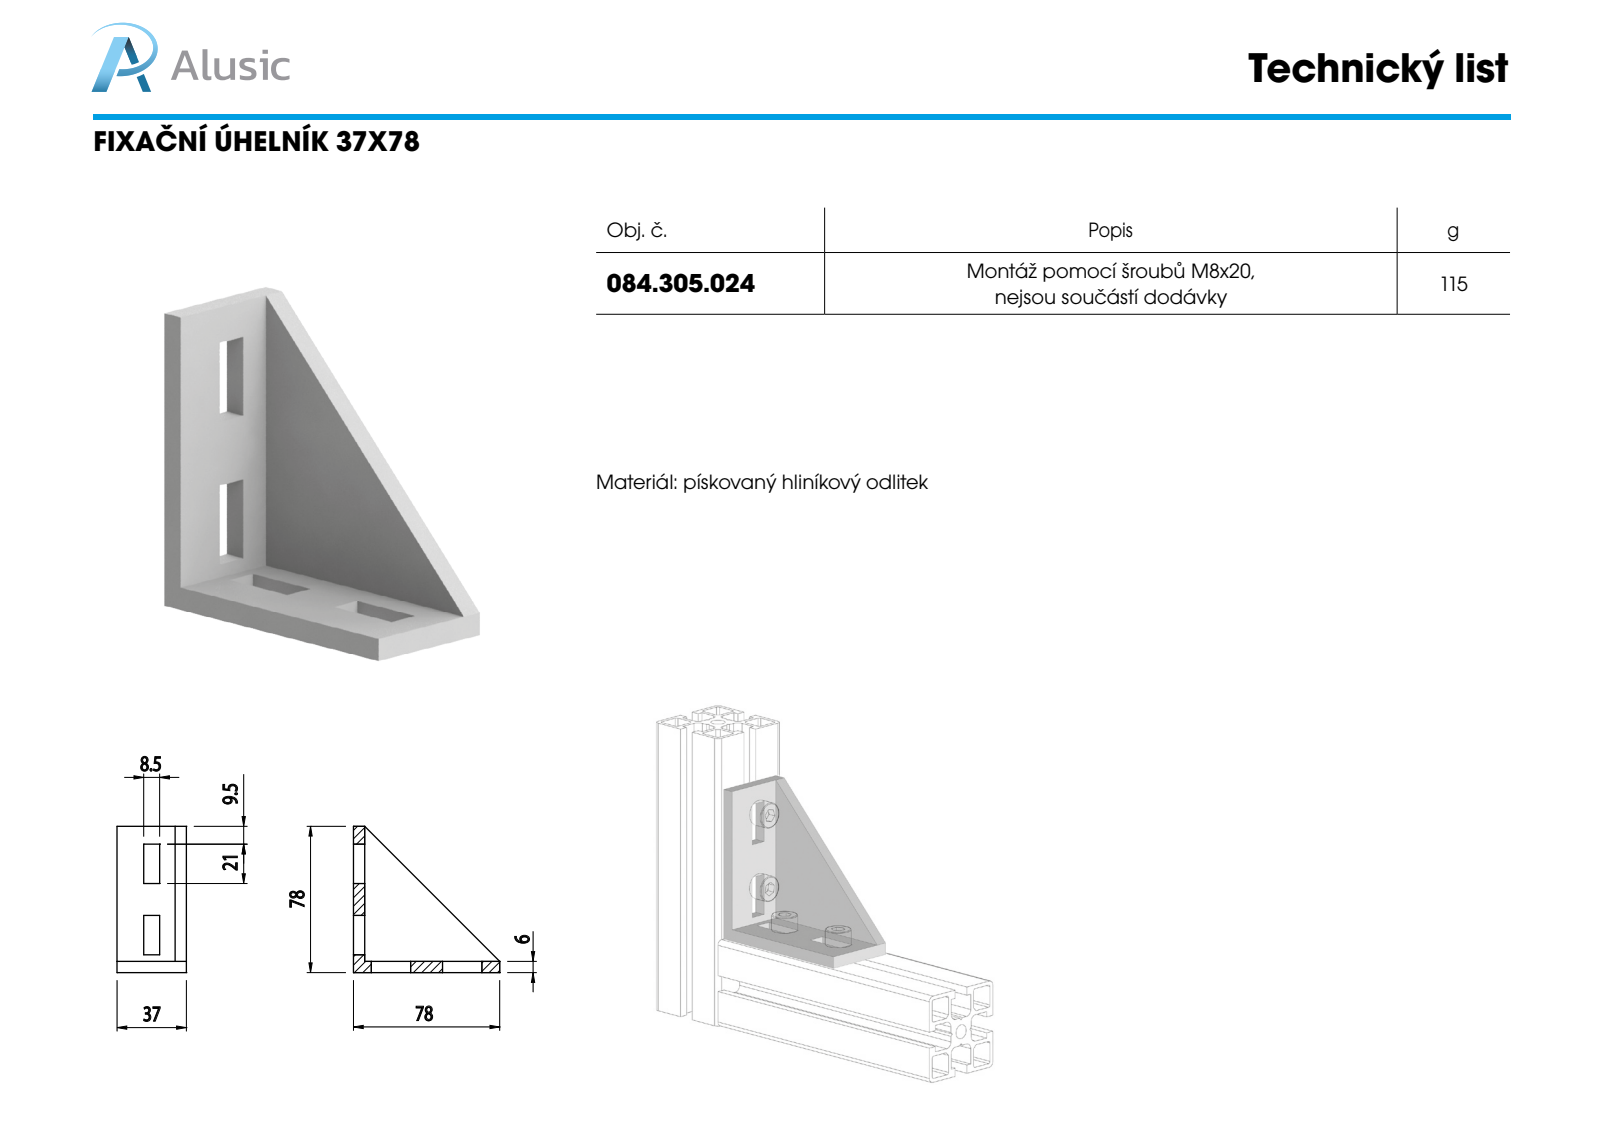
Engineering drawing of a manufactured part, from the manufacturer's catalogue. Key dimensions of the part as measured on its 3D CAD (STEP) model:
Part name (STEP PRODUCT): 084.305.024
STEP written by: SolidWorks 2011 (CONFIG_CONTROL_DESIGN)
Units: millimetres
Bodies: 1 solid, 26 faces (26 planar, 0 cylindrical, 0 other)
Overall size (bounding box): 78 × 78 × 37
Volume: 44 568 mm³ · Surface area: 18 263 mm²
Main face-to-face distances: 6, 14.25, 22.75, 37, 31, 16.75, 8.25, 8.5, 78, 72
